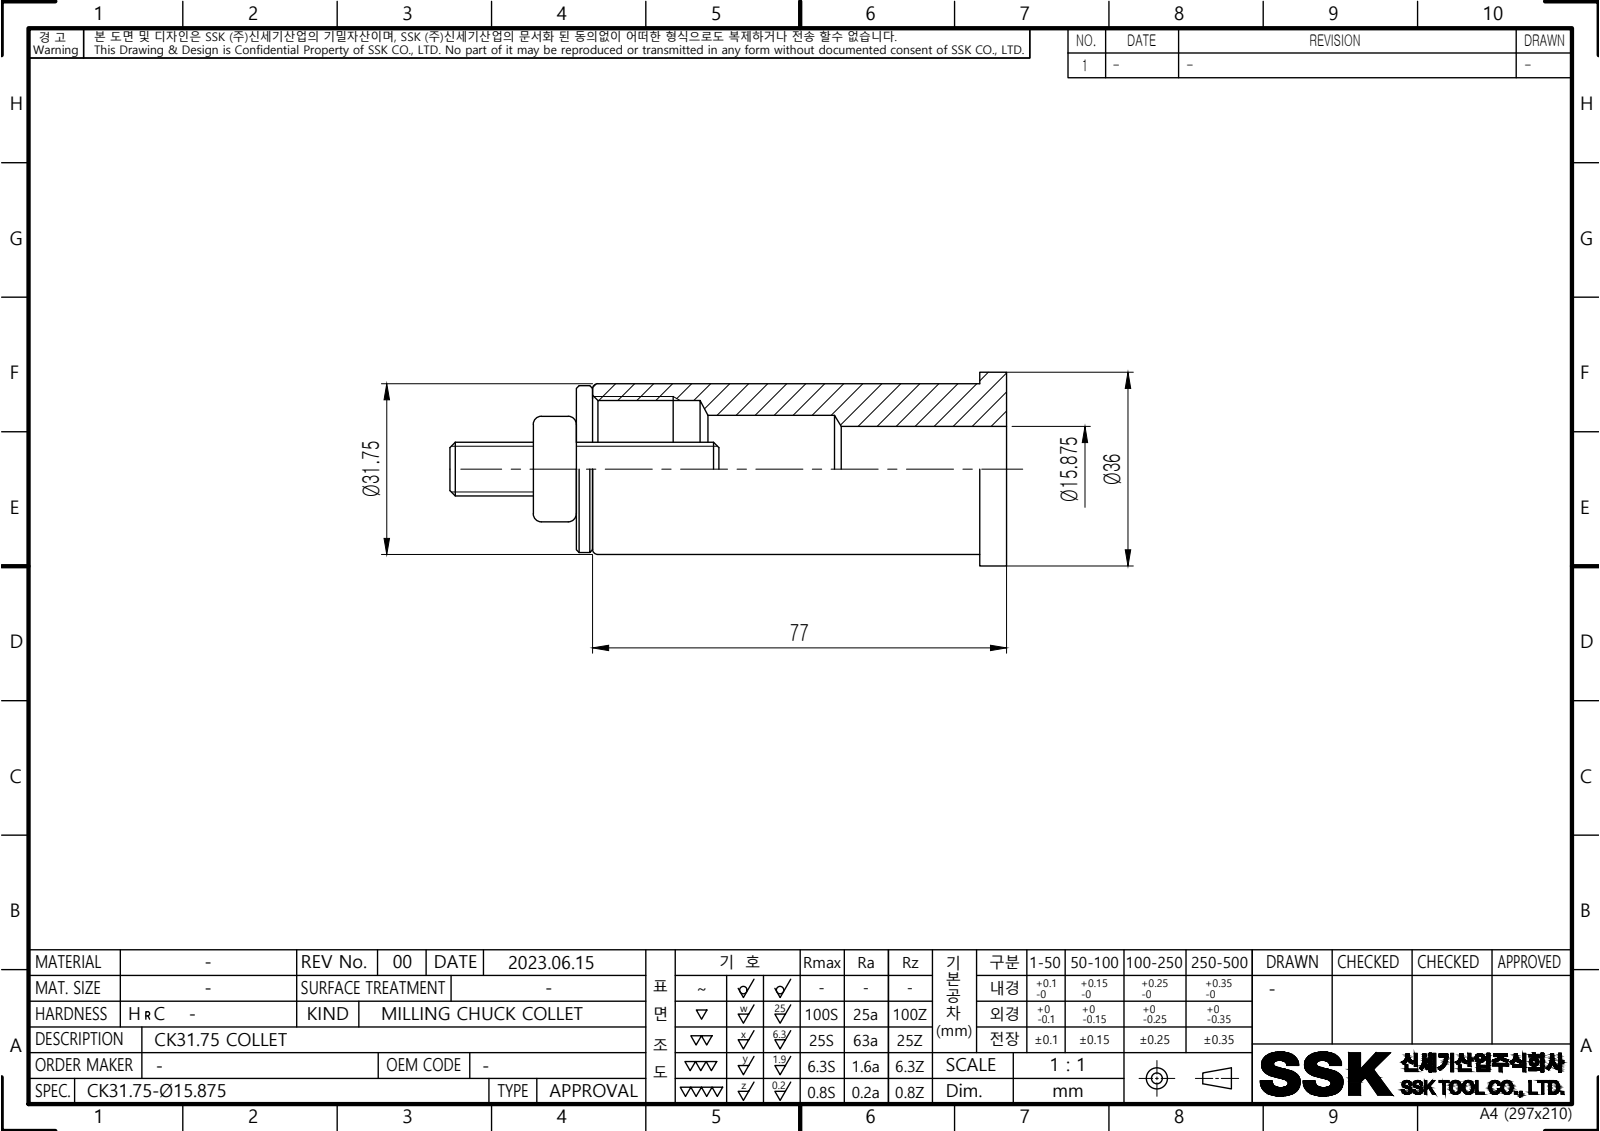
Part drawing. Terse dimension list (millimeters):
name: LO-CK31.75-15.875
written by: Autodesk Inventor 2022 (AUTOMOTIVE_DESIGN)
unit: mm
bodies: 1 solid, 10 faces (3 planar, 5 cylindrical, 2 other)
size: 77 × 36 × 36
volume: 37 573 mm³; area: 14 036 mm²
holes: 1× ⌀15.88, 1× ⌀20, 1× ⌀25.38
bosses: 1× ⌀36, 1× ⌀31.75
face distances: 77, 72, 5
